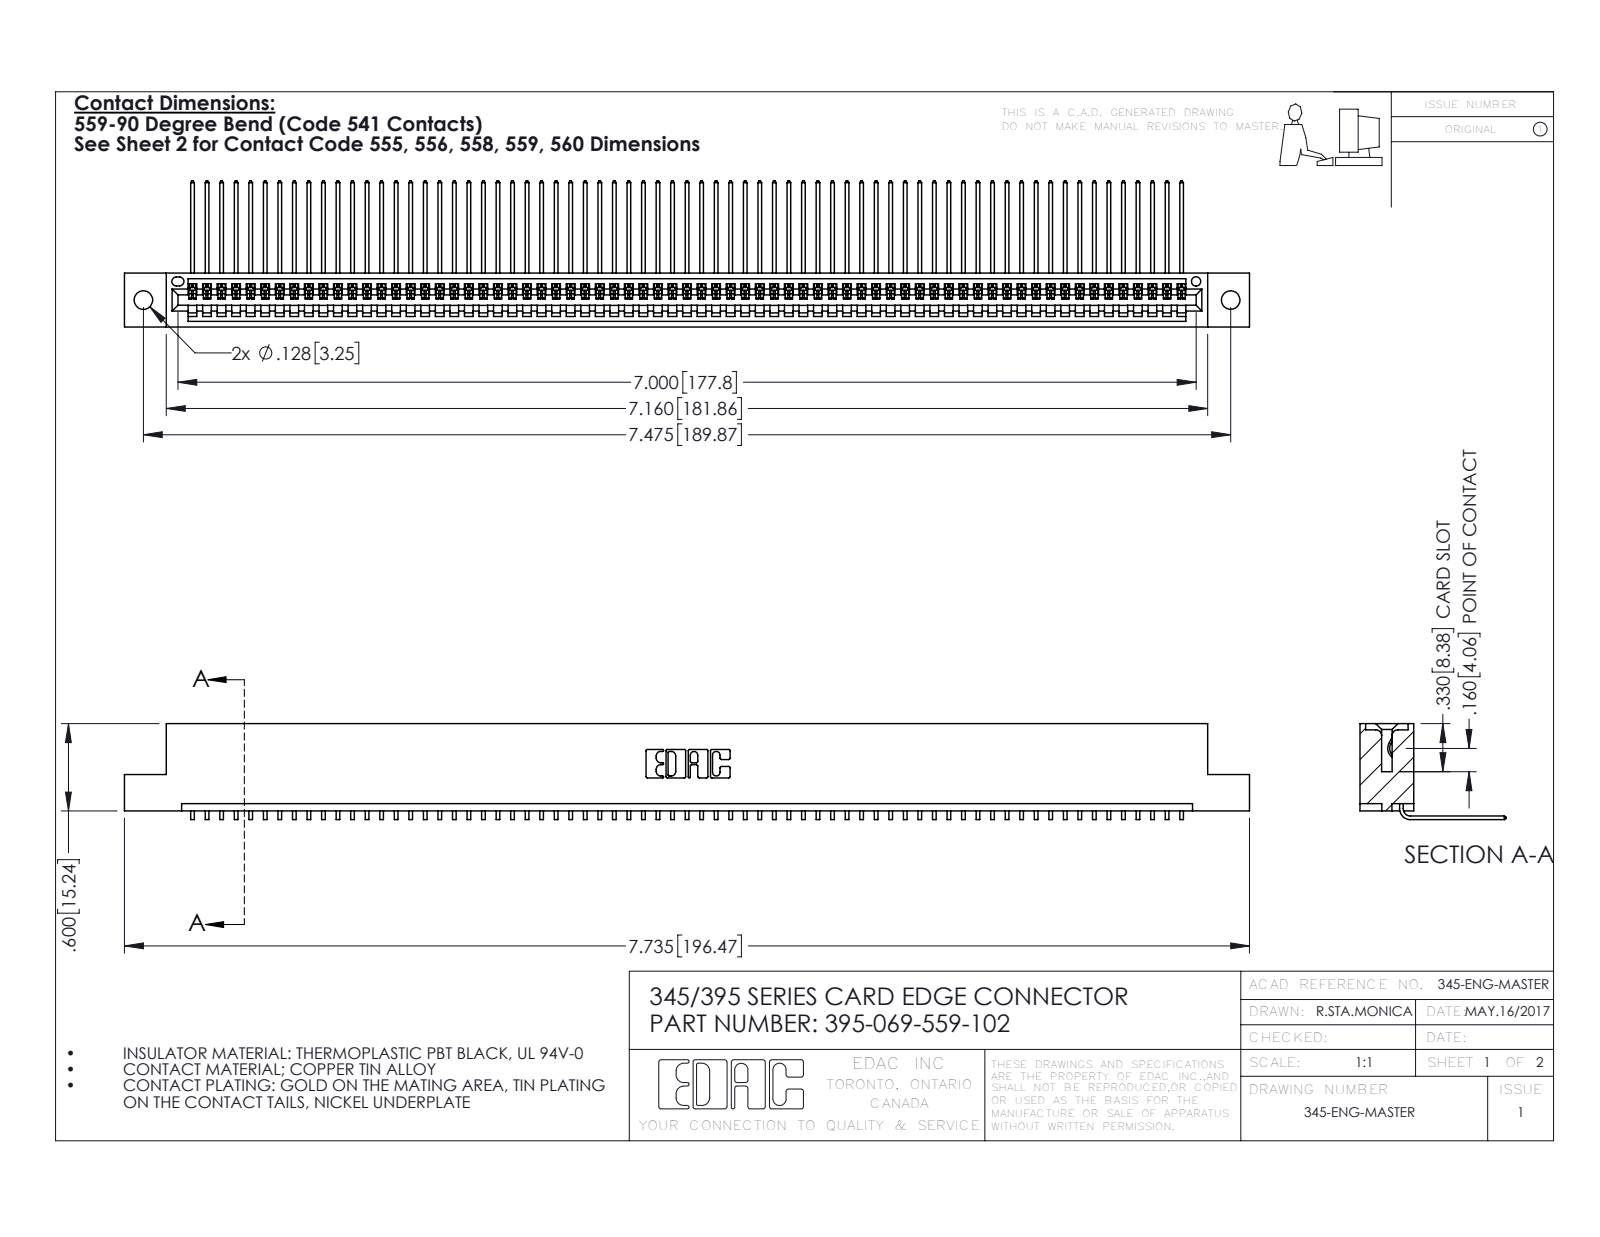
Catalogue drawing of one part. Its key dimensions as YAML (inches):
part_name: "395-069-559-102; 345-292-001_558 559 Tail - 1; 345 Part_Flush Mounting Lugs - 0.128 Dia"
step_written_by: "SolidWorks 2016 (CONFIG_CONTROL_DESIGN)"
units: inches
bodies: {solids: 70, faces: 4266, planar: 2978, cylindrical: 1288, other: 0}
overall_size: [7.735, 1.005, 0.659]
volume: 1.164
surface_area: 41.53
round_holes:
  - {diameter: 0.128, count: 2}
  - {diameter: 0.064, count: 1}
partial_cylinders:
  - {radius: 0.006, count: 138}
  - {radius: 0.01, count: 22}
  - {radius: 0.007, count: 6}
  - {radius: 0.031, count: 6}
  - {radius: 0.026, count: 3}
  - {radius: 0.031, count: 2}
  - {radius: 0.04, count: 2}
  - {radius: 0.014, count: 1}
face_to_face_distances: [0.298, 0.072, 0.37, 0.2, 0.098, 0.272, 0.025, 0.225, 0.149, 0.072]
hole_center_spacings: [0.27, 7.239, 7.475]
